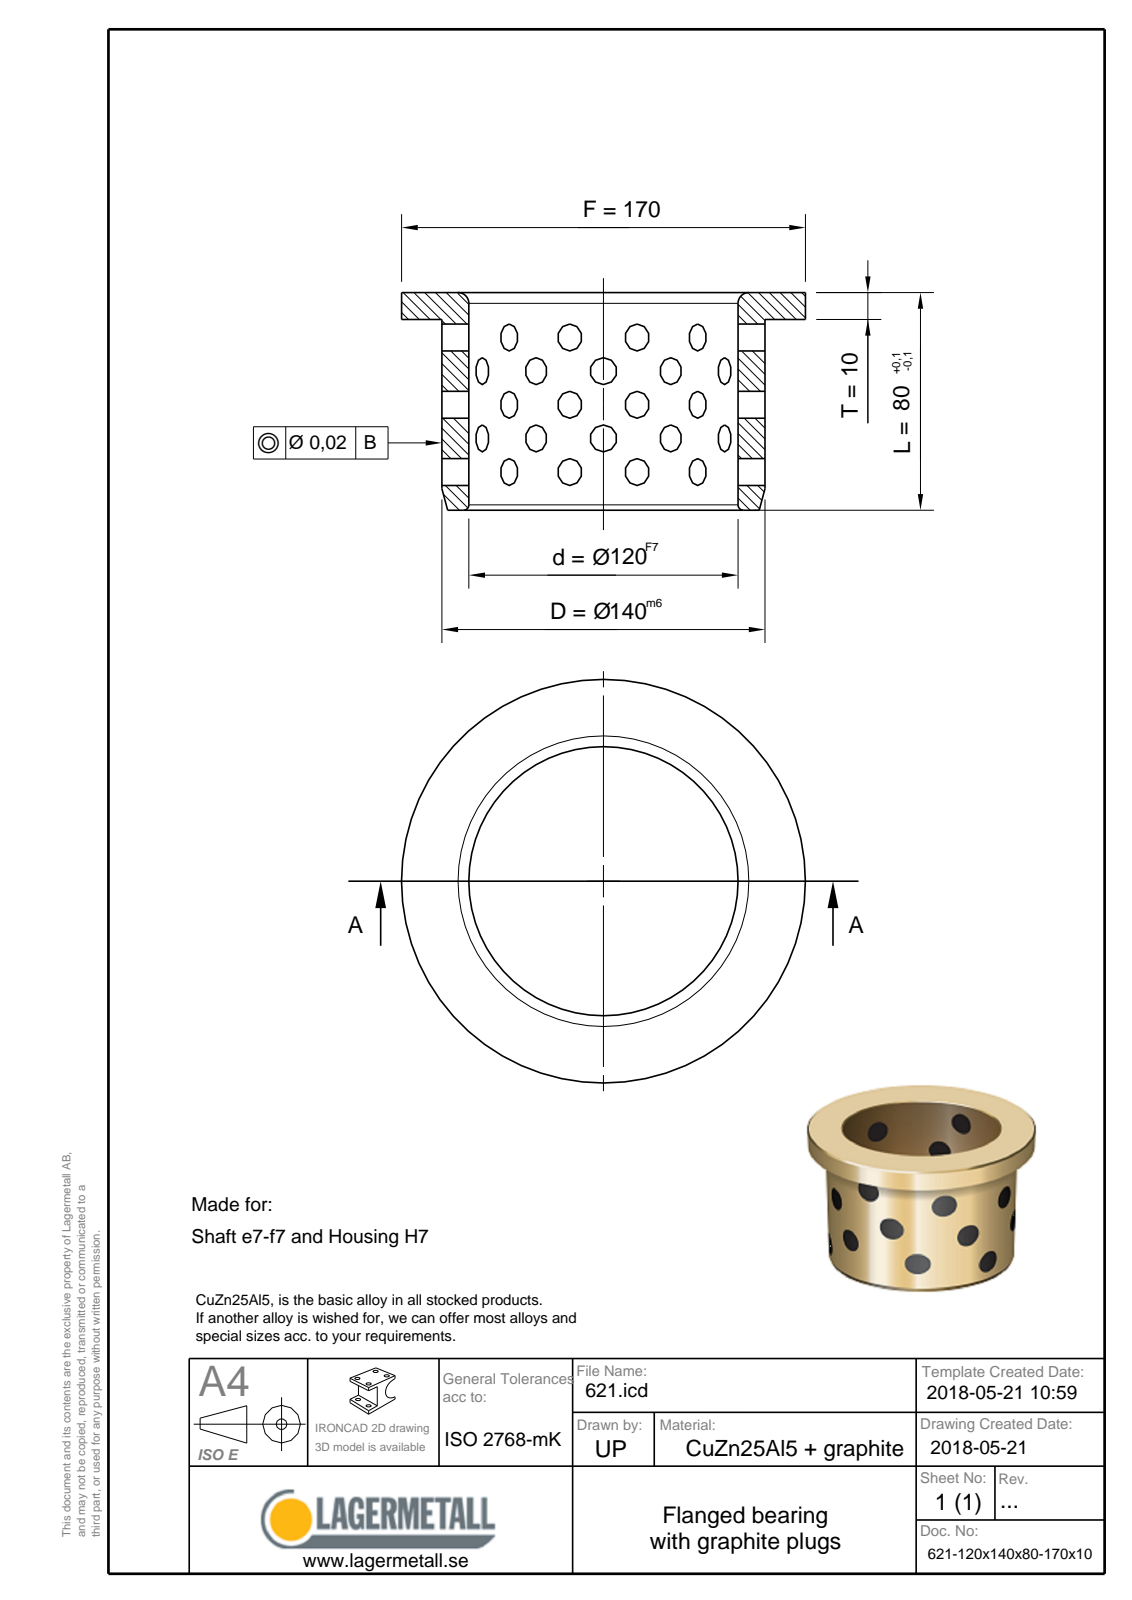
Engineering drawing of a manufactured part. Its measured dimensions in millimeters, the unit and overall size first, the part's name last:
Units: millimetres
Overall size (bounding box): 170 × 170 × 80
Round holes (diameter × count): ⌀120 ×1
Round bosses / shafts (diameter × count): ⌀170 ×1, ⌀140 ×1
Main face-to-face distances: 10, 70, 80
Volume: 397 781 mm³ · Surface area: 87 773 mm²
Bodies: 1 solid, 9 faces (3 planar, 3 cylindrical, 3 other)
Part name (STEP PRODUCT): 621-120x140x80-170x10
STEP written by: Spatial InterOp 3D (CONFIG_CONTROL_DESIGN)
